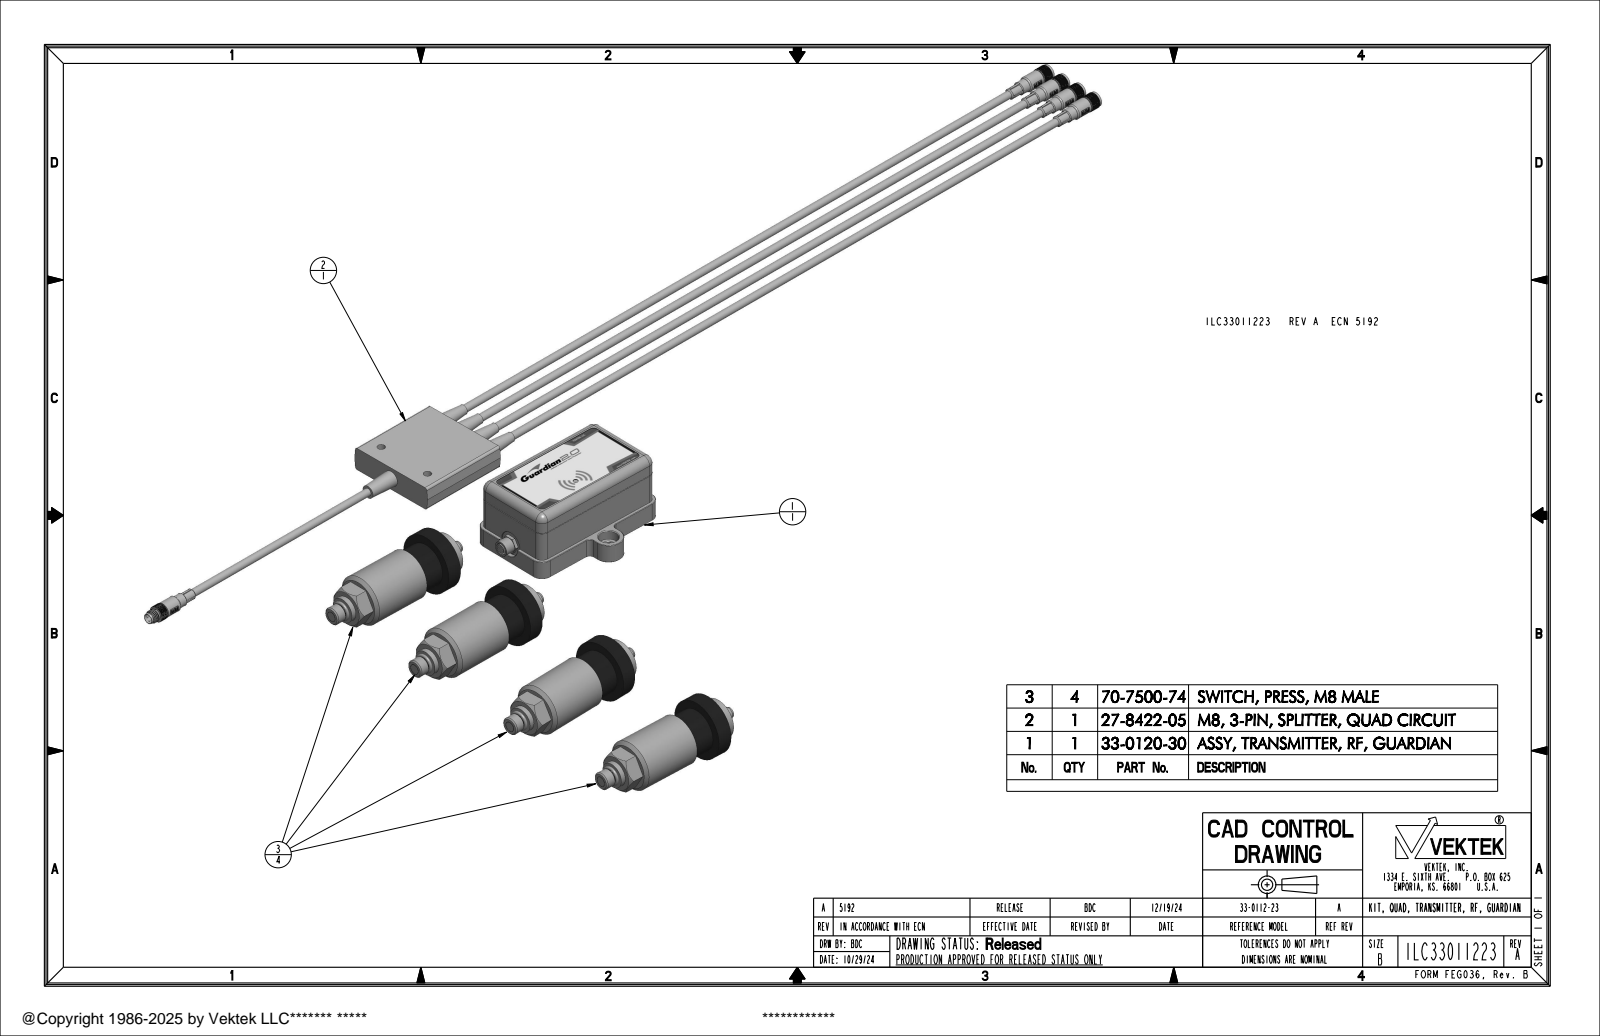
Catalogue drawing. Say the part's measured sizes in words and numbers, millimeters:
The part is named "27842205; 33012030P; 29950000; 33012030 (+2 more)". Its 3-D file was written by "CREO PARAMETRIC BY PTC INC, 2021164 (AUTOMOTIVE_DESIGN)". It is 11 solids with 3074 faces: 1596 planar, 863 cylindrical and 615 other. Overall it measures 760.3 by 361.7 by 46.8 millimeters. Its volume is 465 700 cubic millimeters and its surface area 127 900 square millimeters. Round holes: 12 of diameter 1, 12 of diameter 1.2, 4 of diameter 3.5, 4 of diameter 6.4, 4 of diameter 6.9, 4 of diameter 22.2, 3 of diameter 0.8, 3 of diameter 7, 2 of diameter 5.1, 2 of diameter 11.9, 2 of diameter 12, 1 of diameter 3.3. Round bosses or shafts: 5 of diameter 9.7, 5 of diameter 6.7, 5 of diameter 5, 4 of diameter 38.1, 4 of diameter 31.8, 4 of diameter 27.4, 4 of diameter 25.4, 4 of diameter 15.9. Partial cylindrical surfaces (rounded edges, fillets, slot ends): 8 of radius 0.7, 8 of radius 3, 8 of radius 5, 4 of radius 1.6, 4 of radius 5, 4 of radius 5.4, 4 of radius 5.5, 4 of radius 7. The main face-to-face distances are 15.2, 42.7, 27.5, 52, 2, 9.5, 9.5, 54, 16.7, 7.2. The hole center spacings are 1.8, 13, 26, 2.5, 13.1, 13.1, 3.5, 2.5.
